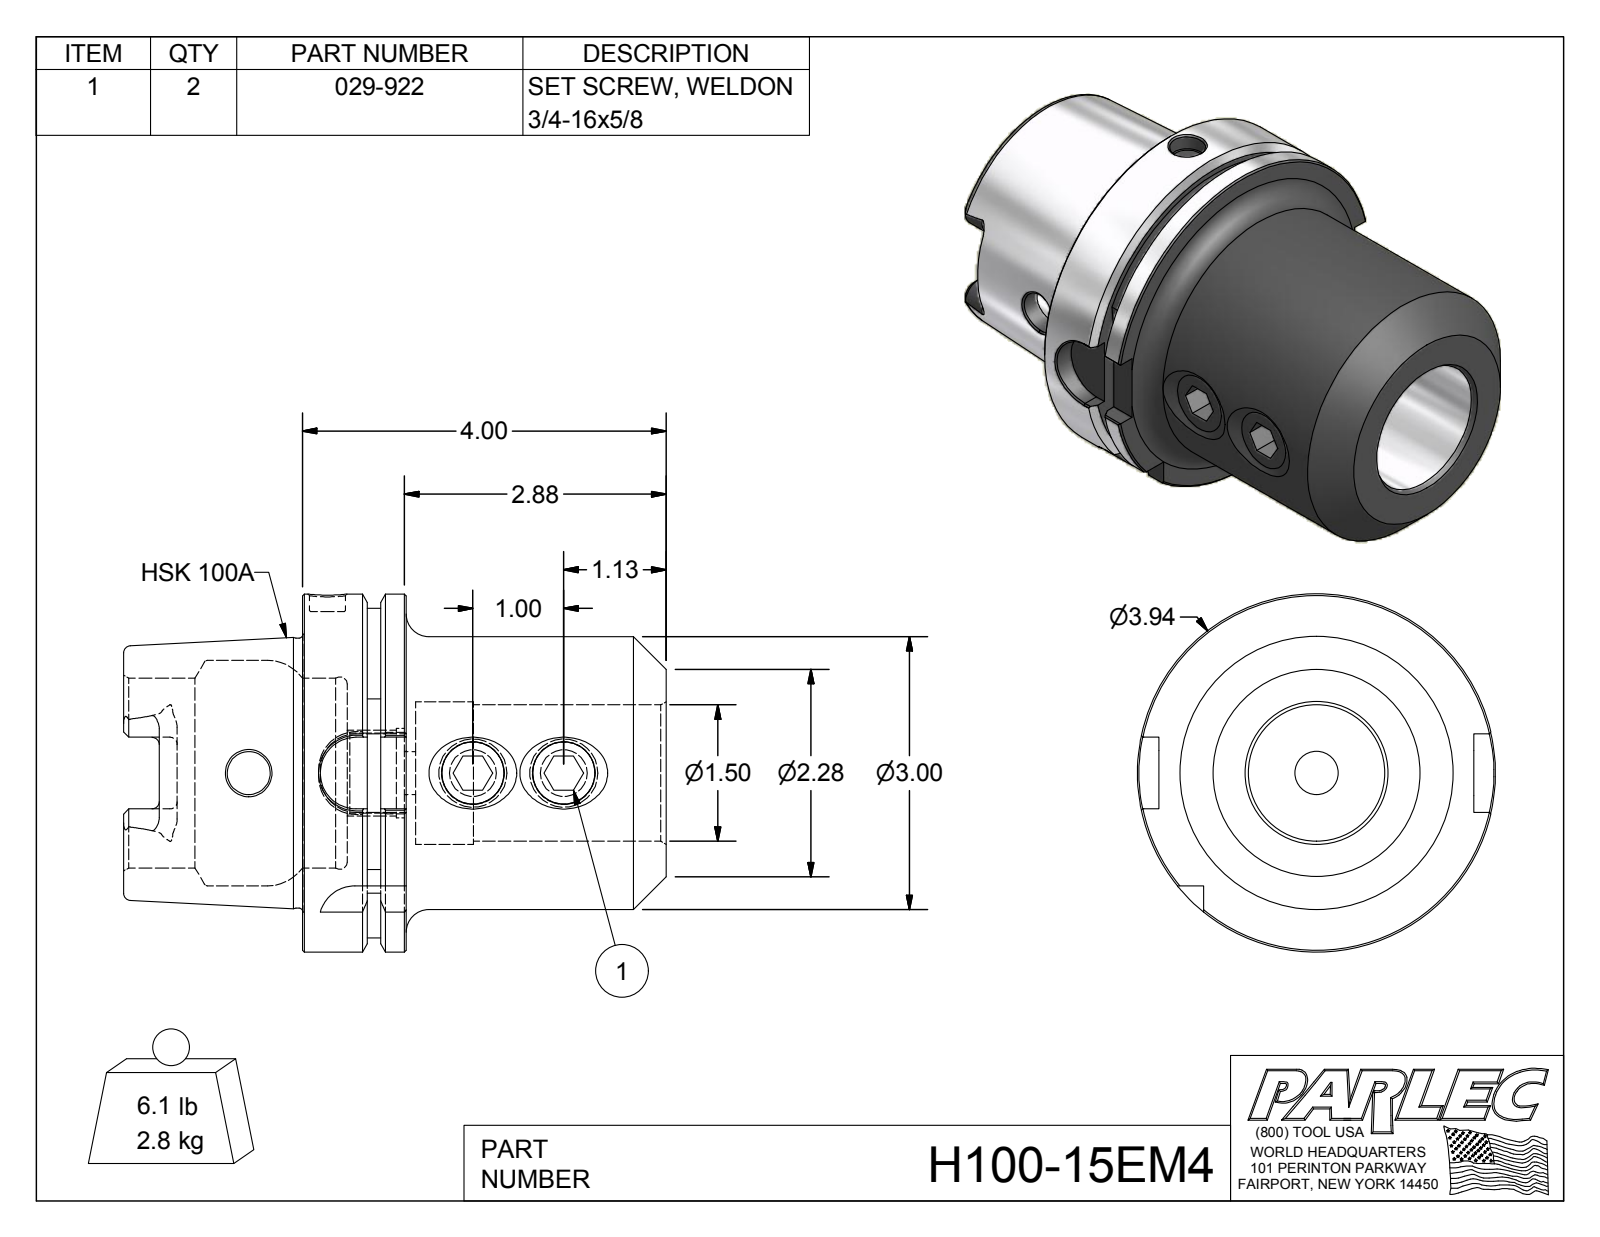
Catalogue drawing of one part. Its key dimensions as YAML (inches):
part_name: "H100-15EM4; 029-922"
step_written_by: "Autodesk Inventor 2012 (AUTOMOTIVE_DESIGN)"
units: inches
bodies: {solids: 3, faces: 154, planar: 63, cylindrical: 38, other: 53}
overall_size: [5.969, 3.937, 3.937]
volume: 30.13
surface_area: 121.4
round_holes:
  - {diameter: 0.472, count: 2}
  - {diameter: 0.682, count: 2}
  - {diameter: 0.394, count: 1}
  - {diameter: 0.881, count: 1}
  - {diameter: 0.985, count: 1}
  - {diameter: 1.5, count: 1}
  - {diameter: 1.569, count: 1}
  - {diameter: 2.087, count: 1}
  - {diameter: 2.48, count: 1}
round_bosses_or_shafts:
  - {diameter: 0.75, count: 2}
  - {diameter: 3.937, count: 1}
  - {diameter: 3, count: 1}
  - {diameter: 2.967, count: 1}
partial_cylinders:
  - {radius: 0.079, count: 6}
  - {radius: 0.192, count: 4}
  - {radius: 0.394, count: 4}
  - {radius: 1.811, count: 1}
face_to_face_distances: [0.492, 4, 3.508, 1.142, 0.65, 2.858, 1.246, 0.754, 0.104, 2.754]
hole_center_spacings: [1, 2.466, 3.466]
